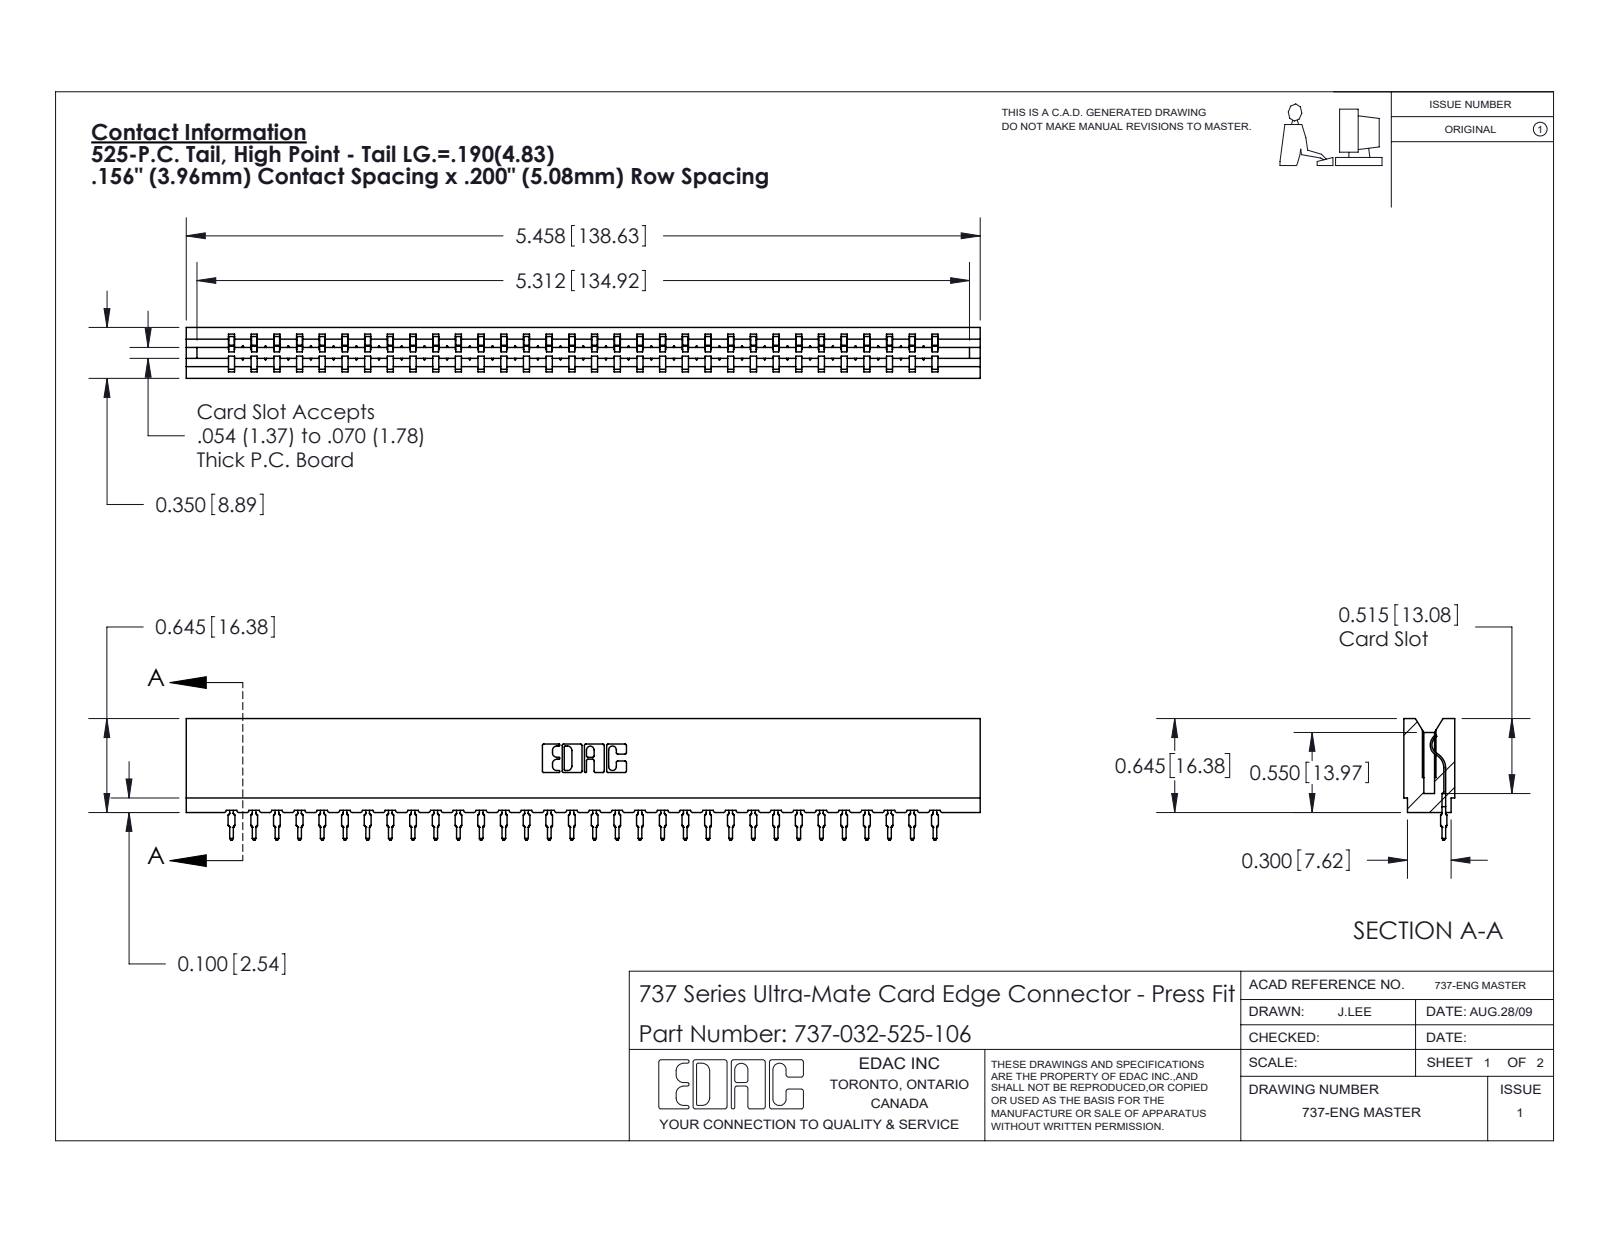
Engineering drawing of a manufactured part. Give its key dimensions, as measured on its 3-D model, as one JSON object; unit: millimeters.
{"part_name": "737 Part_Insulator Option - 06; 737-032-525-106; 745-292-001_525", "step_written_by": "SolidWorks 2020 (CONFIG_CONTROL_DESIGN)", "units": "millimeters", "bodies": {"solids": 33, "faces": 3711, "planar": 2231, "cylindrical": 648, "other": 832}, "overall_size": [138.6, 21.2, 8.9], "volume_mm3": 13400, "surface_area_mm2": 17770, "partial_cylinders_radius": [[0.4, 64], [0.5, 64], [0.3, 22], [0.2, 6], [0.8, 6], [0.1, 4], [0.3, 4], [0.7, 3]], "face_to_face_distances": [3.5, 5.4, 8.9, 1.9, 1.1, 7.7, 2.4, 4.2, 15.8, 4]}
